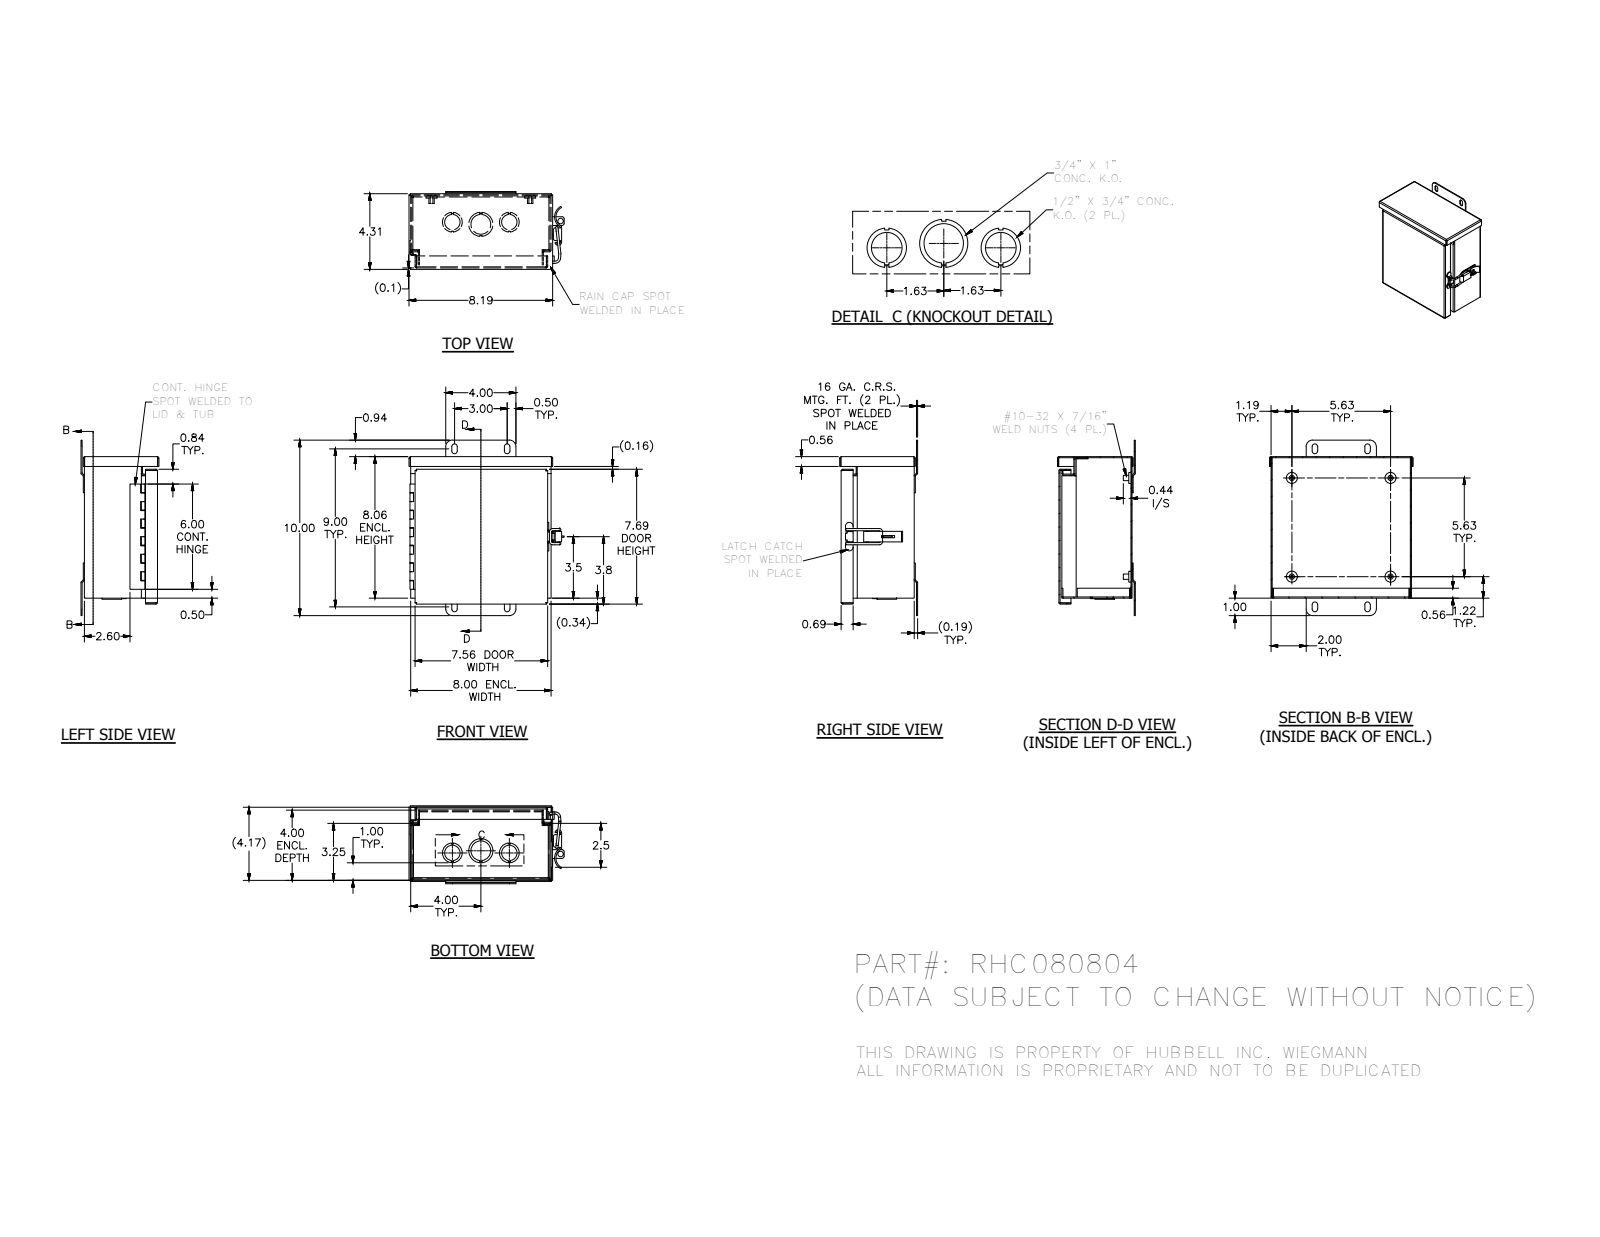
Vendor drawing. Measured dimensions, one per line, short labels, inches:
name: RHC884BKPA; RHC84EWPA; RHC84CPA; RHC08ABOVEDRPA (+8 more)
written by: Autodesk Inventor 2014 (AUTOMOTIVE_DESIGN)
unit: in
bodies: 21 solids, 585 faces (382 planar, 163 cylindrical, 40 other)
size: 10 × 8.844 × 4.44
holes: 4× ⌀0.156, 3× ⌀1.125, 2× ⌀0.875, 1× ⌀0.117, 1× ⌀0.13, 1× ⌀0.315, 1× ⌀1.375
bosses: 8× ⌀0.125, 4× ⌀0.625, 4× ⌀0.3, 1× ⌀0.2, 1× ⌀0.1
rounds: 21× R0.031, 21× R0.094, 8× R0.063, 8× R0.094, 8× R0.156, 6× R0.125, 4× R0.375, 3× R0.031
face distances: 0.063, 4.106, 7.937, 8, 4.169, 4.043, 7.5, 7.875, 8.063, 0.19
hole spacings: 5.625, 5.625, 7.955, 0.616, 1.63, 1.63, 2.78, 2.926
